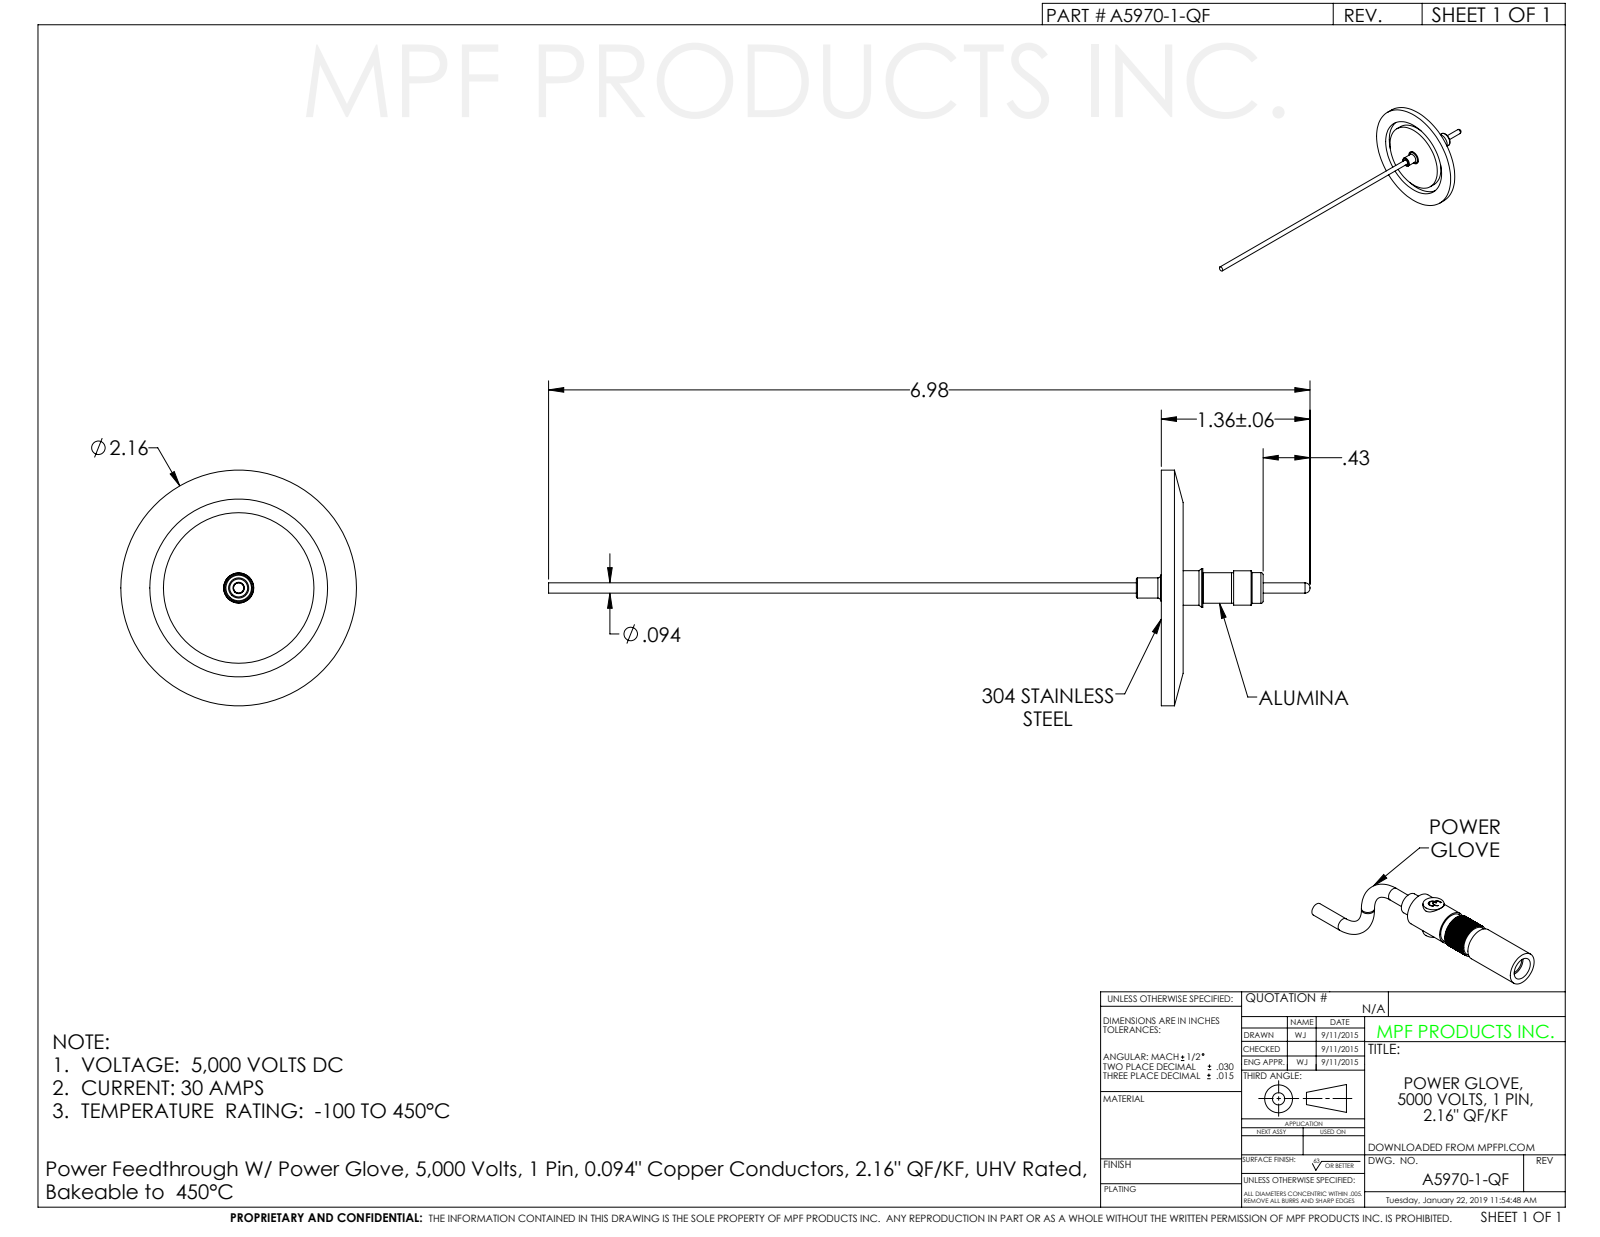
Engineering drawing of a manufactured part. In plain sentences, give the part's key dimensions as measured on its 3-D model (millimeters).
The part is named "A5970-1-QF". Its 3-D file was written by "SolidWorks 2012 (CONFIG_CONTROL_DESIGN)". It is 1 solid with 72 faces: 14 planar, 36 cylindrical and 22 other. Overall it measures 177.3 by 54.9 by 54.9 millimeters. Its volume is 12 000 cubic millimeters and its surface area 8 361 square millimeters. Round holes: 1 of diameter 2.7, 1 of diameter 6.5, 1 of diameter 6.6, 1 of diameter 7, 1 of diameter 7, 1 of diameter 41.2. Round bosses or shafts: 1 of diameter 54.9, 1 of diameter 39.1, 1 of diameter 7.9, 1 of diameter 7.9, 1 of diameter 7.3, 1 of diameter 7.2, 1 of diameter 7.1, 1 of diameter 6.2. The main face-to-face distances are 5.1, 2.5, 2.6, 23.7, 21.3, 18.7, 20.2, 17.7, 15.1, 3.6.
